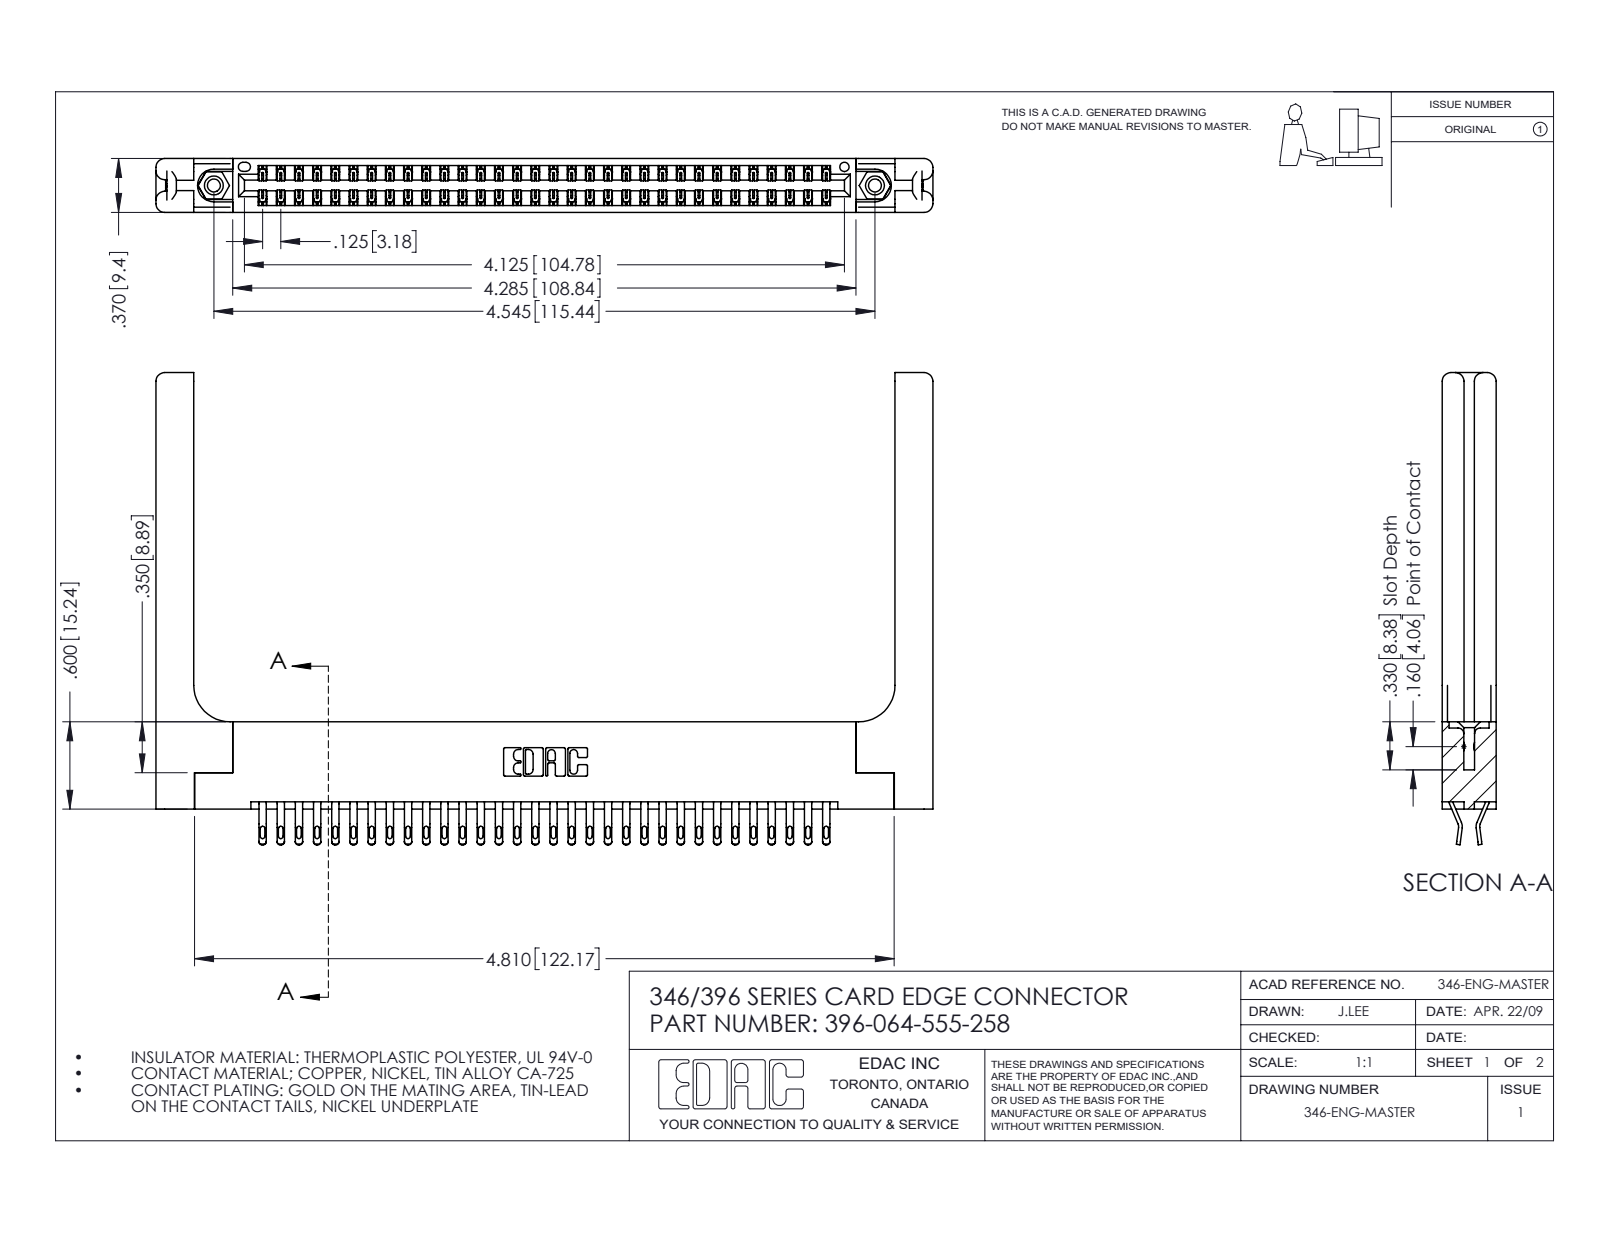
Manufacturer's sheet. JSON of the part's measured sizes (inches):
{"part_name": "345-250-001_345-250-001-102; 396-064-555-258; 346 Part_Flush Mounting Lugs - 0.156 Dia-TH; 346-220-058_345-220-058 (+1 more)", "step_written_by": "SolidWorks 2016 (CONFIG_CONTROL_DESIGN)", "units": "inches", "bodies": {"solids": 69, "faces": 4090, "planar": 2336, "cylindrical": 1694, "other": 60}, "overall_size": [5.341, 3.245, 0.37], "volume_in3": 1.271, "surface_area_in2": 36.9, "round_holes": [[0.089, 2], [0.125, 2], [0.156, 2], [0.064, 1]], "round_bosses_or_shafts": [[0.155, 2]], "partial_cylinders_radius": [[0.016, 128], [0.02, 128], [0.006, 96], [0.01, 22], [0.06, 16], [0.007, 6], [0.031, 6], [0.026, 3]], "face_to_face_distances": [0.37, 0.048, 0.322, 0.072, 0.148, 0.15, 0.25, 0.025, 0.298, 0.275], "hole_center_spacings": [0.246, 4.337, 4.545]}
